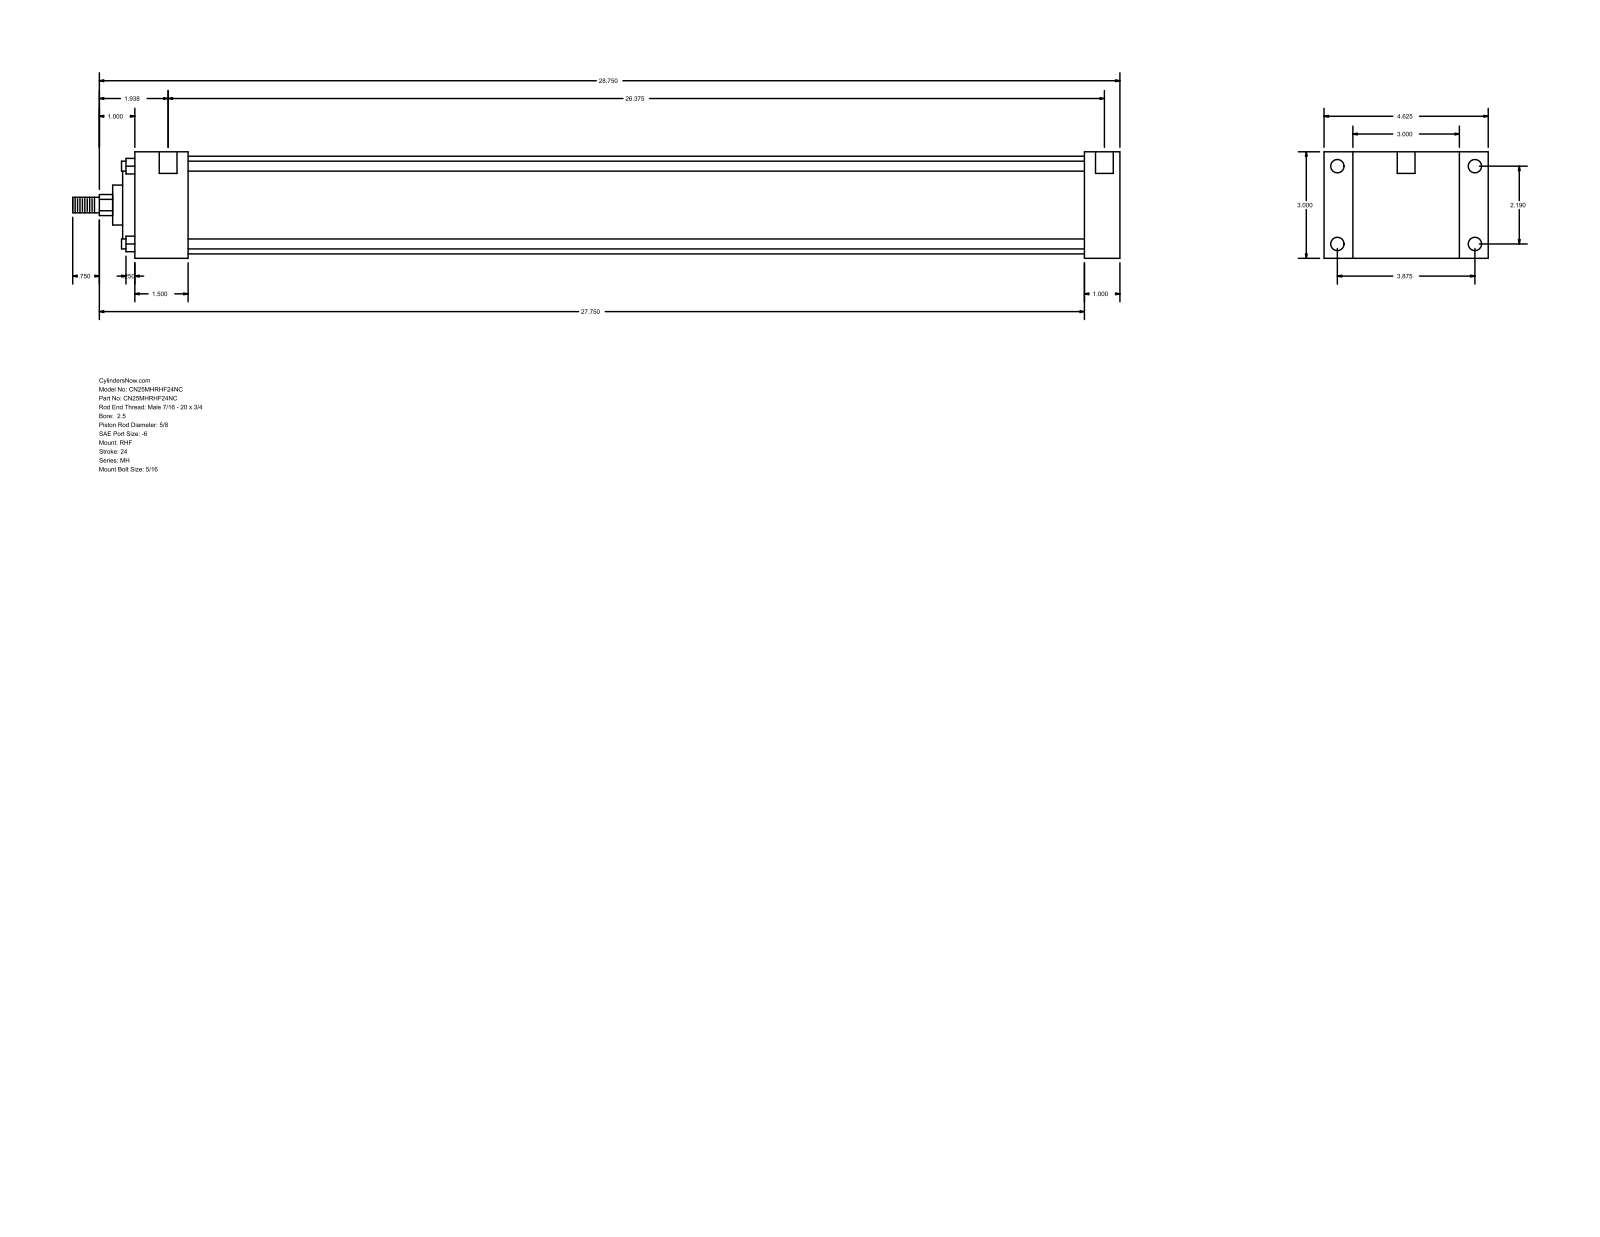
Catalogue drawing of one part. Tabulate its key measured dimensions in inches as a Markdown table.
| quantity | value |
| --- | --- |
| part name | MH_RHF__0250_0.625 |
| STEP written by | GSSL Pune (CONFIG_CONTROL_DESIGN) |
| units | inches |
| bodies | 0 solids, 90 faces (61 planar, 29 cylindrical, 0 other) |
| overall size | 29.5 × 4.625 × 3 |
| round holes (diameter × count) | 0.219 × 4, 0.375 × 4, 0.5 × 2 |
| round bosses / shafts (diameter × count) | 0.281 × 4, 2.75 × 1, 2.187 × 1, 1.125 × 1, 0.625 × 1, 0.437 × 1 |
| partial cylindrical surfaces (radius × count) | 0.297 × 1 |
| main face-to-face distances | 3, 1, 0.813, 3.813, 27.75, 26.75, 1.5, 4.625, 25.25, 26.25 |
| hole center spacings | 2.19, 3.875, 4.451, 26.687, 0.125, 0.187, 26.375, 26.5 |
